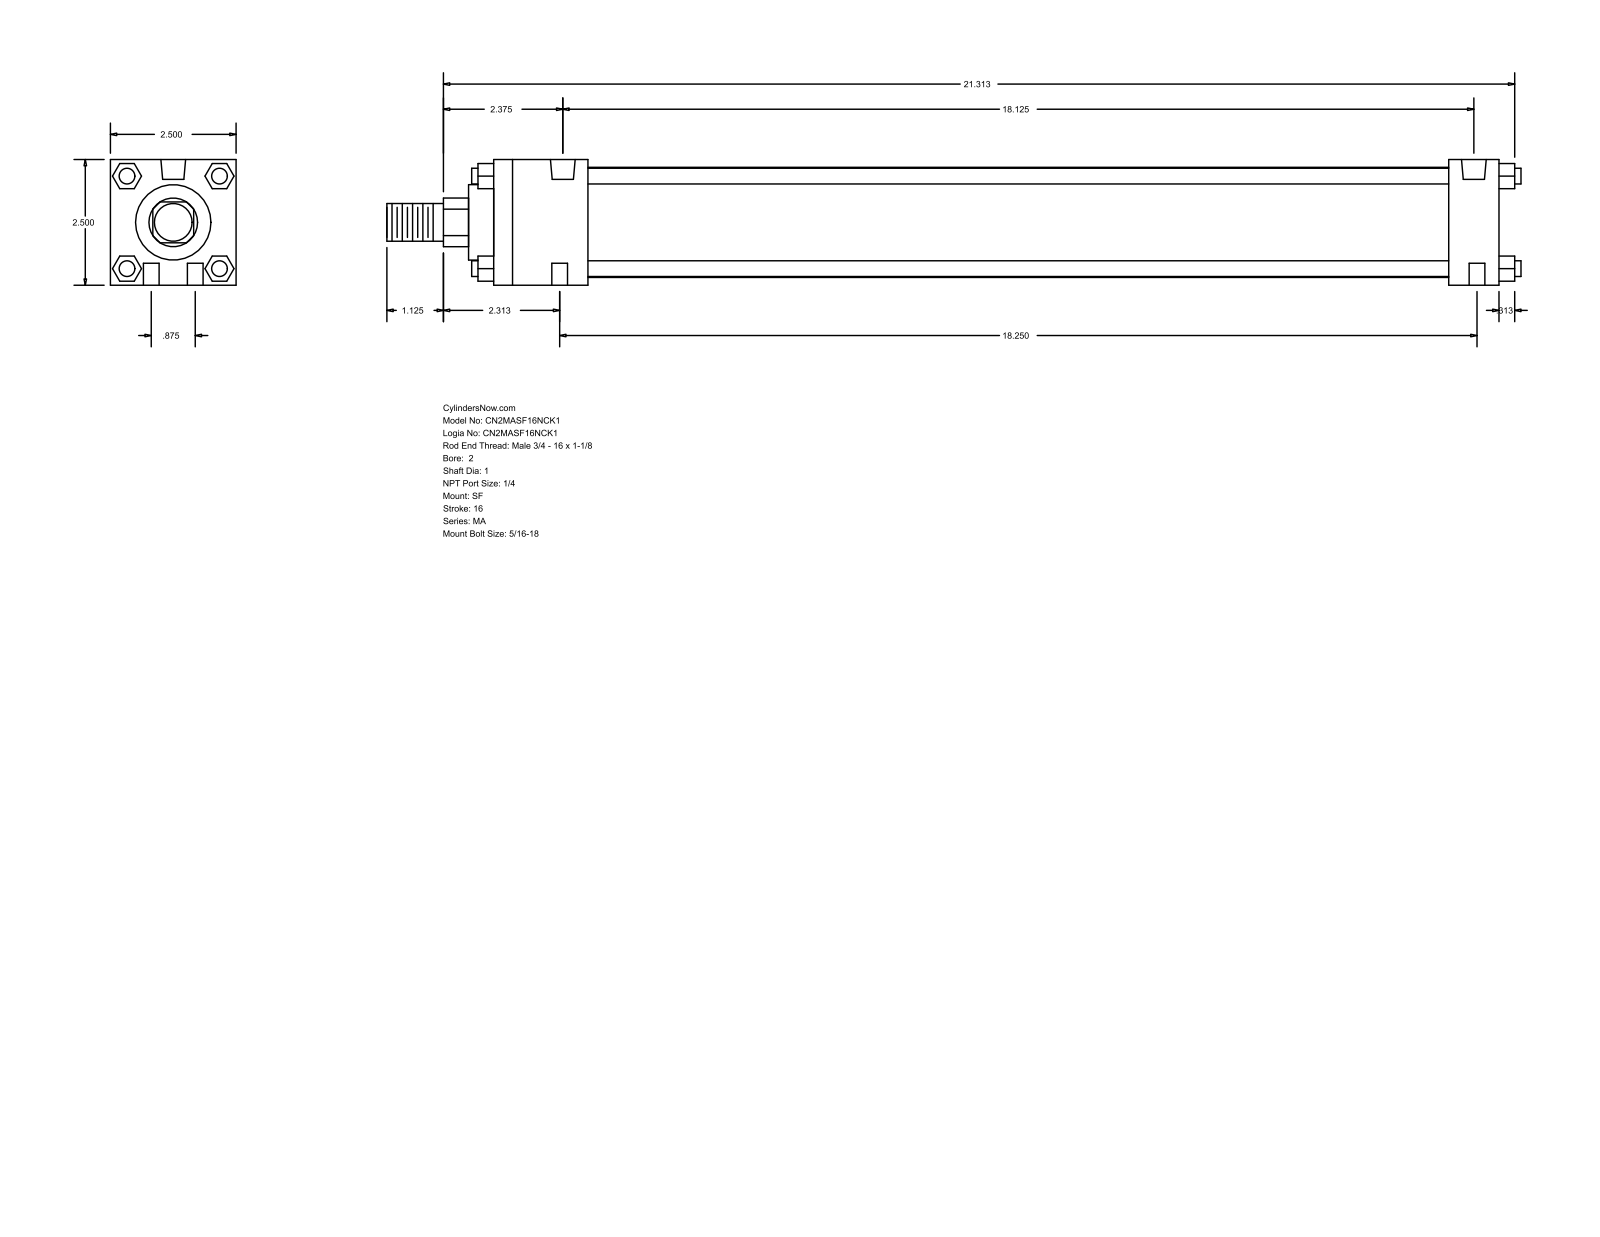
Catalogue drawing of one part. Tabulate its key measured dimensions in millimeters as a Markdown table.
| quantity | value |
| --- | --- |
| part name | MA_SF__0200_1 |
| STEP written by | GSSL Pune (CONFIG_CONTROL_DESIGN) |
| units | millimeters |
| bodies | 0 solids, 124 faces (94 planar, 30 cylindrical, 0 other) |
| overall size | 573.09 × 63.5 × 63.5 |
| round holes (diameter × count) | 7.94 × 6, 12.49 × 2 |
| round bosses / shafts (diameter × count) | 7.94 × 4, 55.63 × 1, 38.1 × 1, 25.4 × 1, 19.05 × 1 |
| partial cylindrical surfaces (radius × count) | 12.29 × 1 |
| main face-to-face distances | 63.5, 508, 12.7, 25.4, 482.6, 47.63, 434.97, 460.37, 23.37, 40.47 |
| hole center spacings | 11.22, 462.09, 22.22, 460.37, 463.55, 464.08 |
